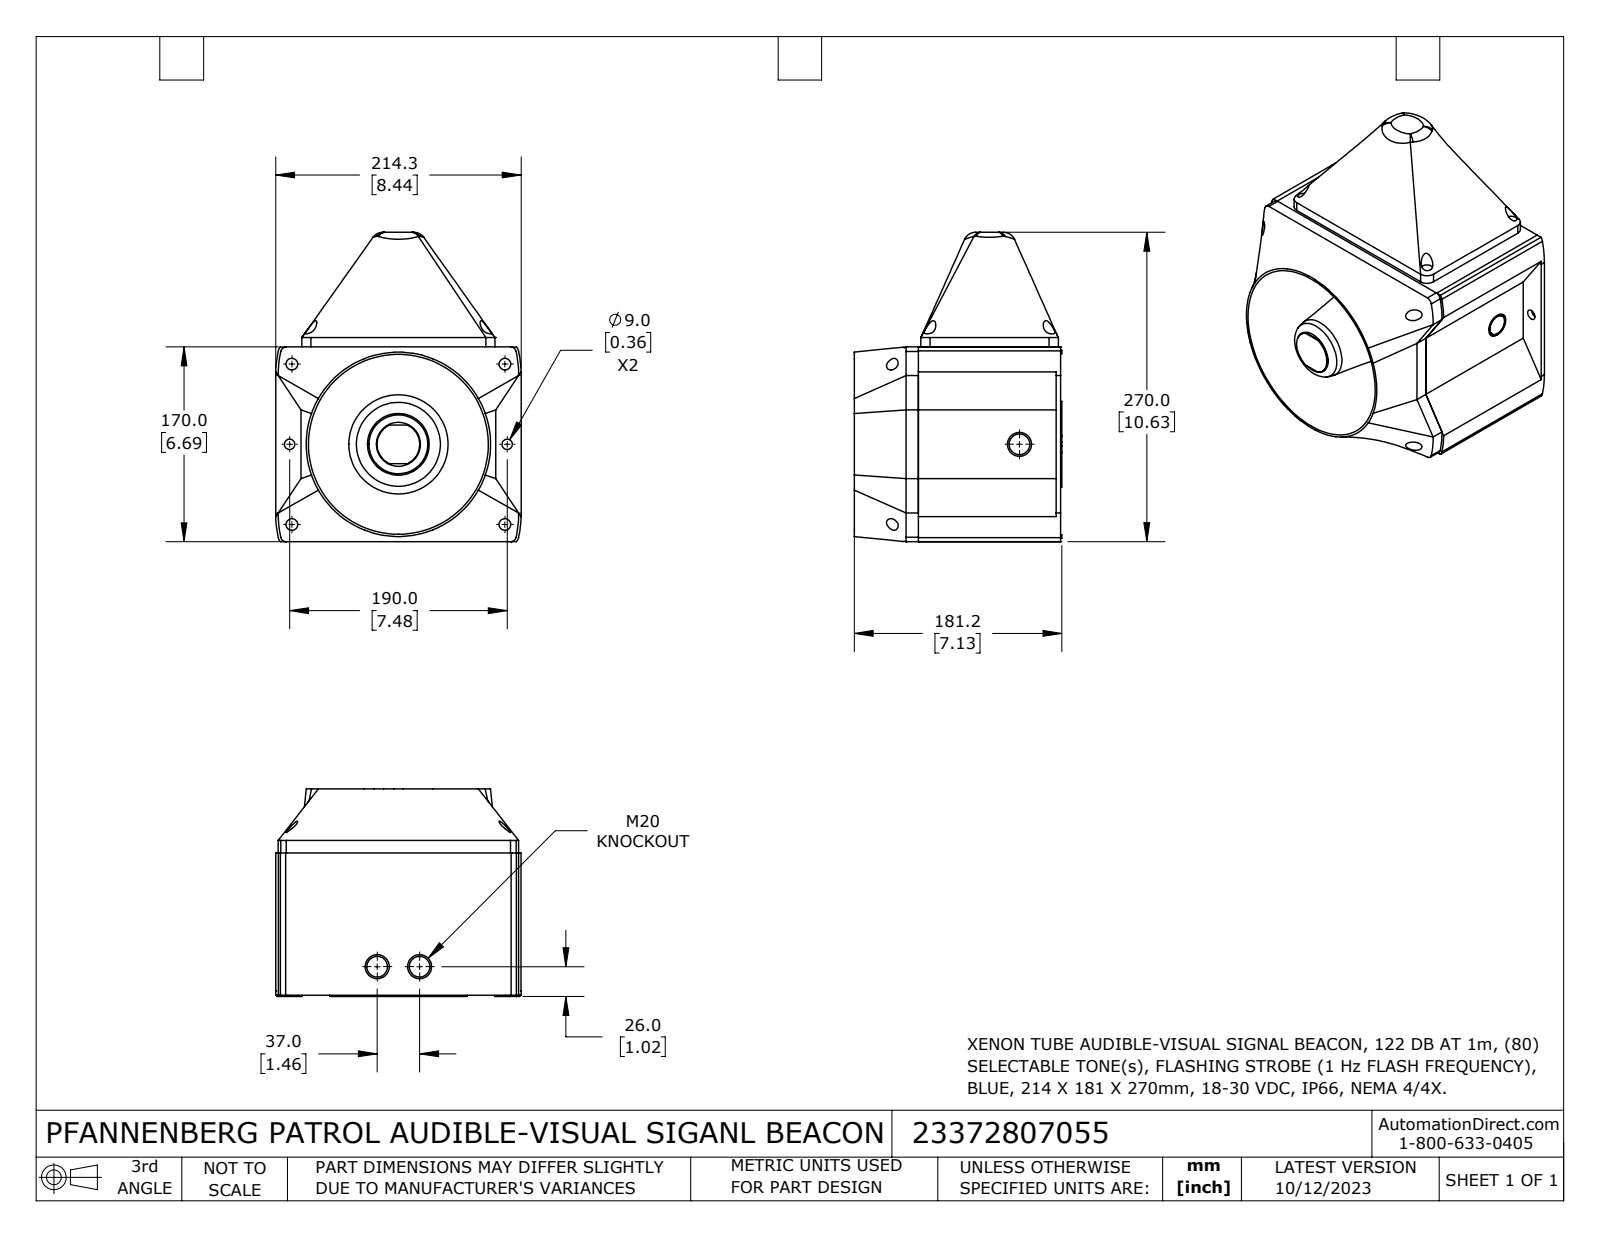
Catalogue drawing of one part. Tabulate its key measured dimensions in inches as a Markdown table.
| quantity | value |
| --- | --- |
| part name | 23372807055 |
| STEP written by | SolidWorks 2023 (CONFIG_CONTROL_DESIGN) |
| units | inches |
| bodies | 4 solids, 192 faces (92 planar, 64 cylindrical, 36 other) |
| overall size | 10.63 × 8.438 × 7.134 |
| volume | 315.4 in³ |
| surface area | 690 in² |
| round holes (diameter × count) | 0.402 × 8, 0.827 × 3, 0.356 × 2, 5.5 × 1 |
| round bosses / shafts (diameter × count) | 0.709 × 3, 6.339 × 1 |
| partial cylindrical surfaces (radius × count) | 0.197 × 4, 0.282 × 4, 3.937 × 4, 4.022 × 4, 0.295 × 2 |
| main face-to-face distances | 4.89, 6.692, 6.691, 2.844, 2.045, 4, 0.89, 1.955, 6.693, 2.205 |
| hole center spacings | 2.757, 4.583, 7.898, 2.353, 3.74, 3.781, 4.094, 4.183 |
